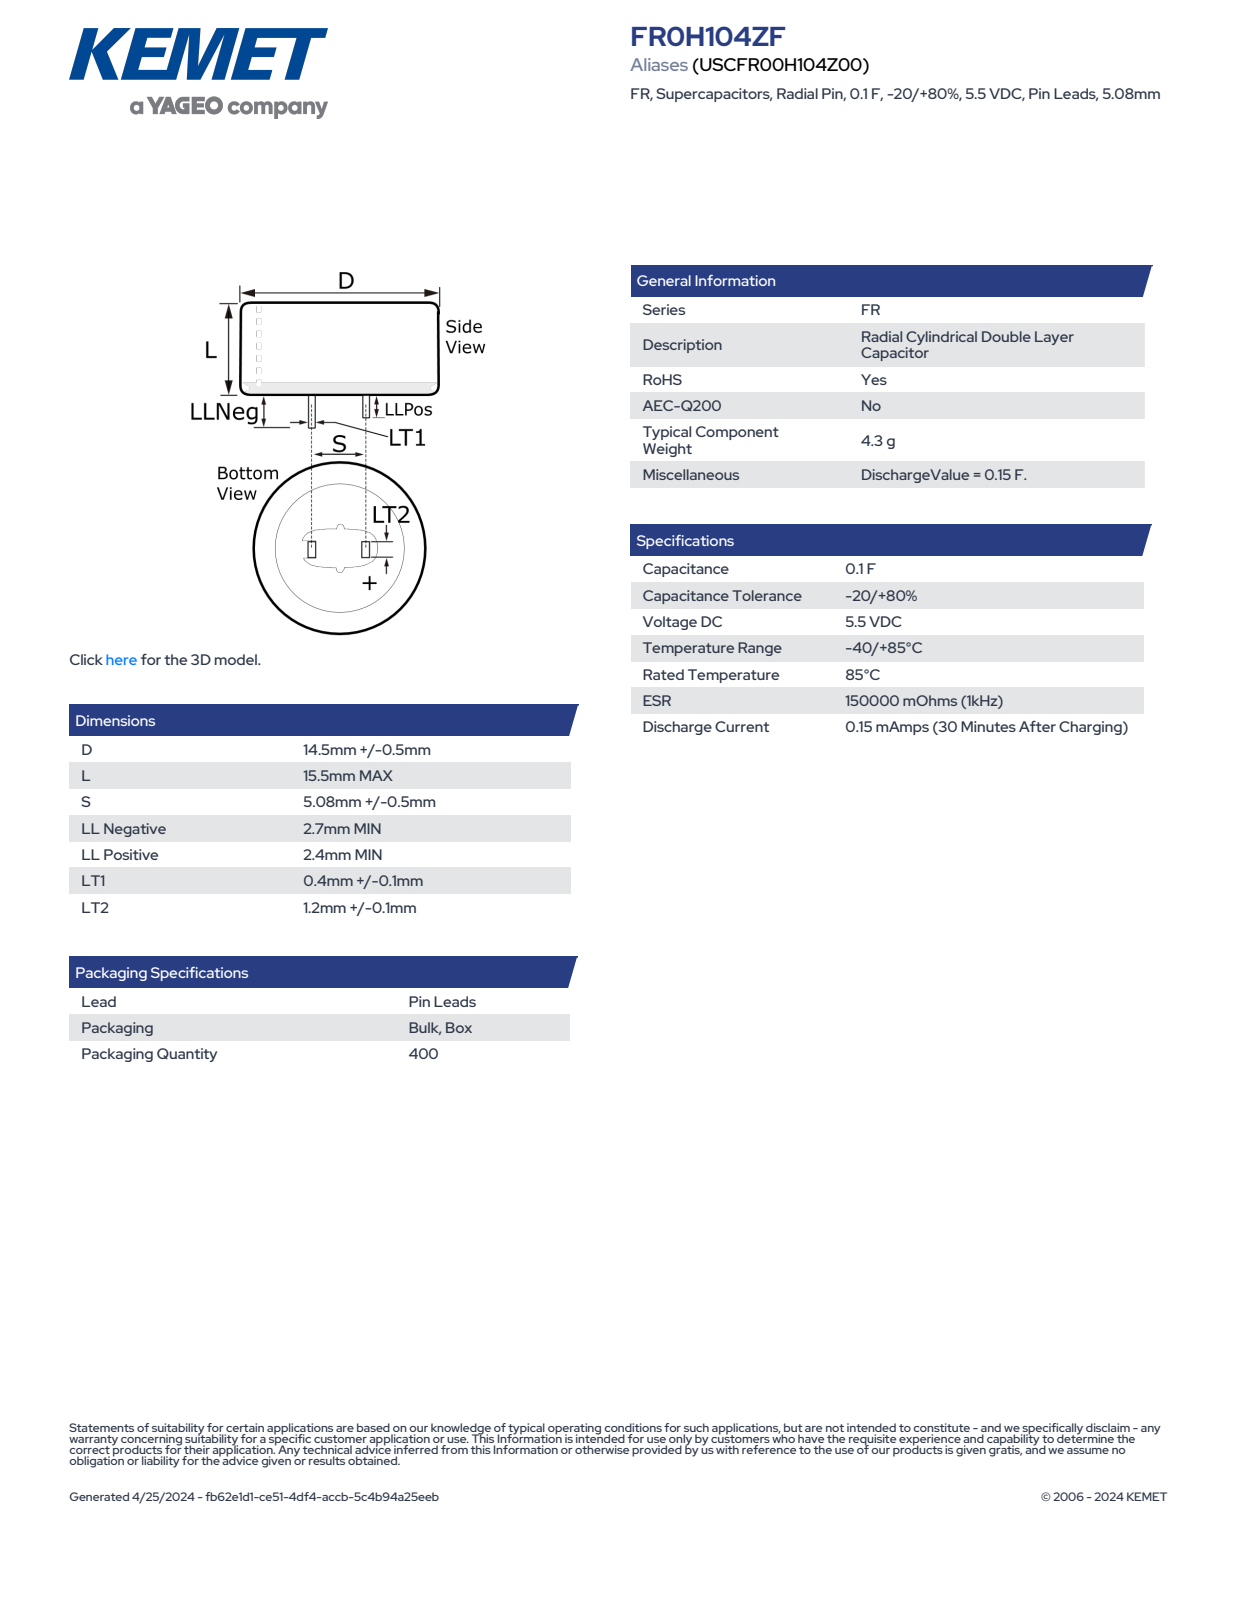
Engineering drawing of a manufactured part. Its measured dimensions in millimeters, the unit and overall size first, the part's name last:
Units: millimetres
Overall size (bounding box): 18.2 × 15 × 15
Round bosses / shafts (diameter × count): ⌀15 ×1
Partial cylindrical surfaces — rounded edges, fillets, slot ends (radius × count): R7.51 ×1
Main face-to-face distances: 15.5, 15.49, 0.5, 5.08, 5.58, 4.58, 1.3, 2.7, 18.19, 18.2
Volume: 2 723 mm³ · Surface area: 1 062 mm²
Bodies: 1 solid, 78 faces (70 planar, 4 cylindrical, 4 other)
Part name (STEP PRODUCT): CDR_LPLLN_D15L15.5S5.08LLNEG2.7LLPOS2.4LT10.5LT21.3
STEP written by: SolidWorks 2014 (AUTOMOTIVE_DESIGN)
